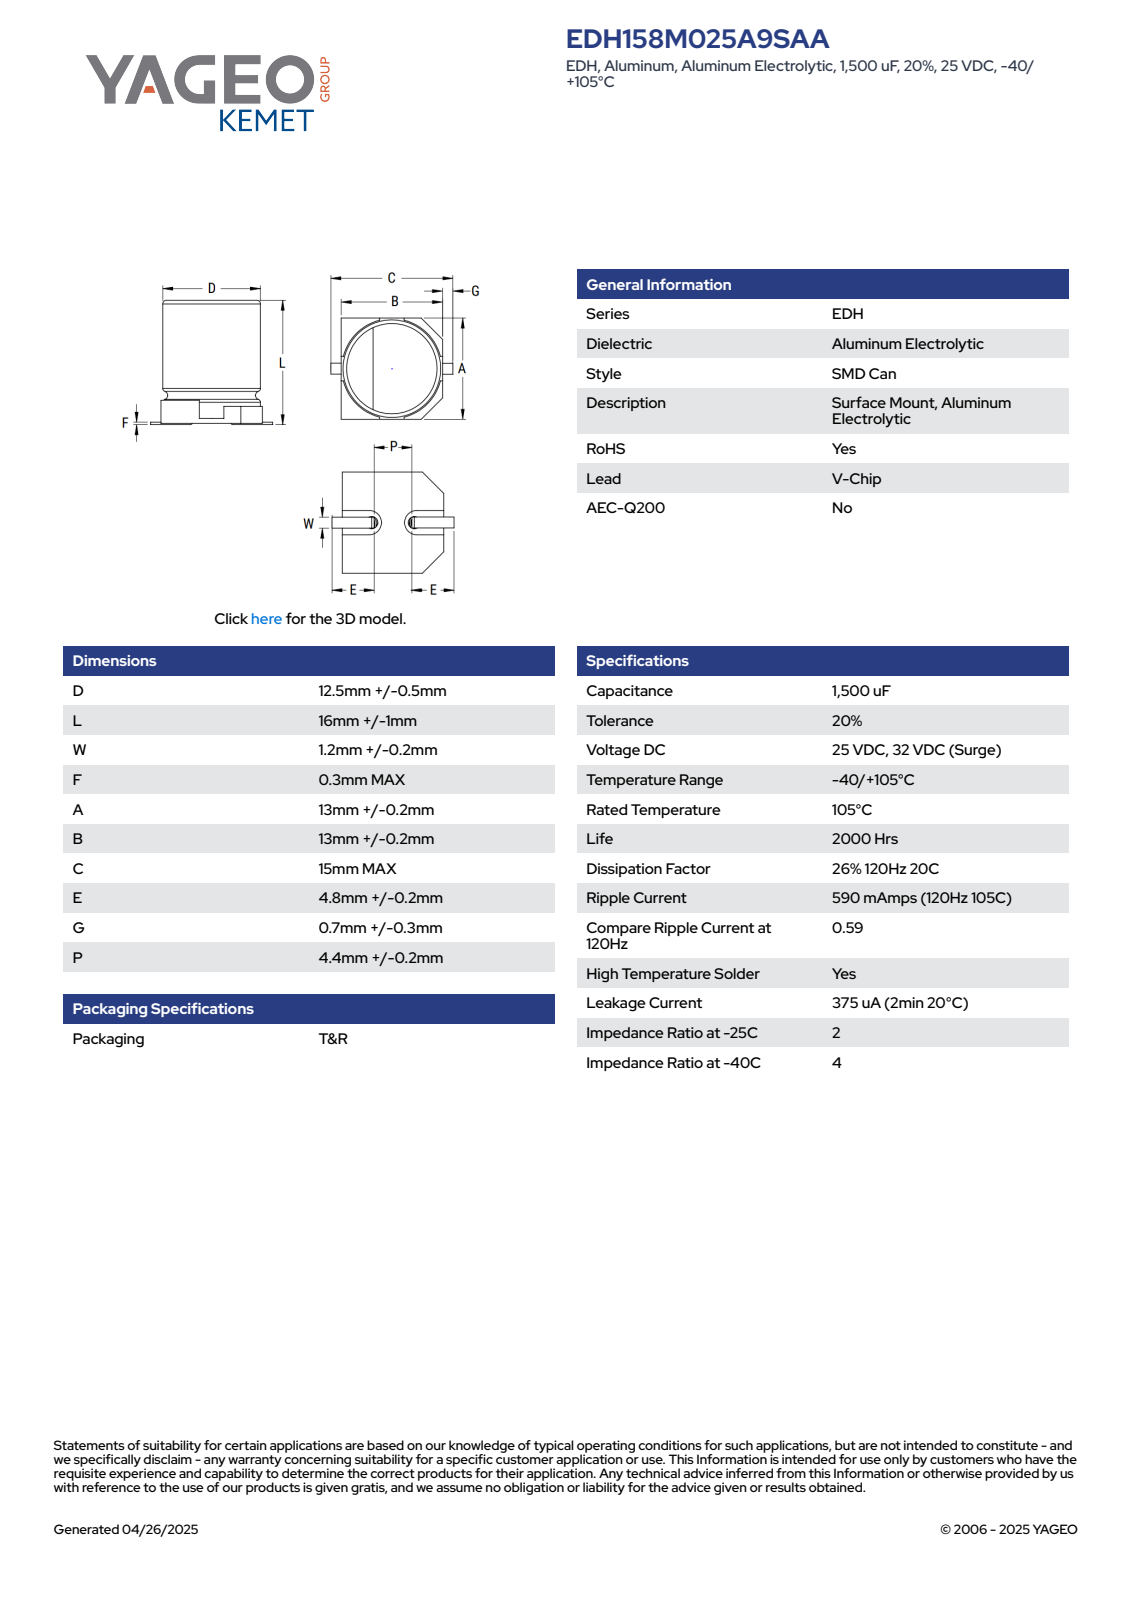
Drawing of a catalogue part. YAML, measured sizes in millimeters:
part_name: "CAC_S_12.5X16_D13L16.5W1.45F0.3A13B13C15.2E5.1P4.8"
step_written_by: "SolidWorks 2014 (AUTOMOTIVE_DESIGN)"
units: millimeters
bodies: {solids: 5, faces: 78, planar: 61, cylindrical: 11, other: 6}
overall_size: [16.5, 15, 13]
volume: 2044
surface_area: 1400
round_bosses_or_shafts:
  - {diameter: 12.43, count: 1}
partial_cylinders:
  - {radius: 0.2, count: 2}
  - {radius: 5.16, count: 1}
  - {radius: 6.5, count: 1}
face_to_face_distances: [0.82, 16.2, 15.38, 16.21, 15.39, 13, 3.3, 4.12, 12.08, 12.09]
